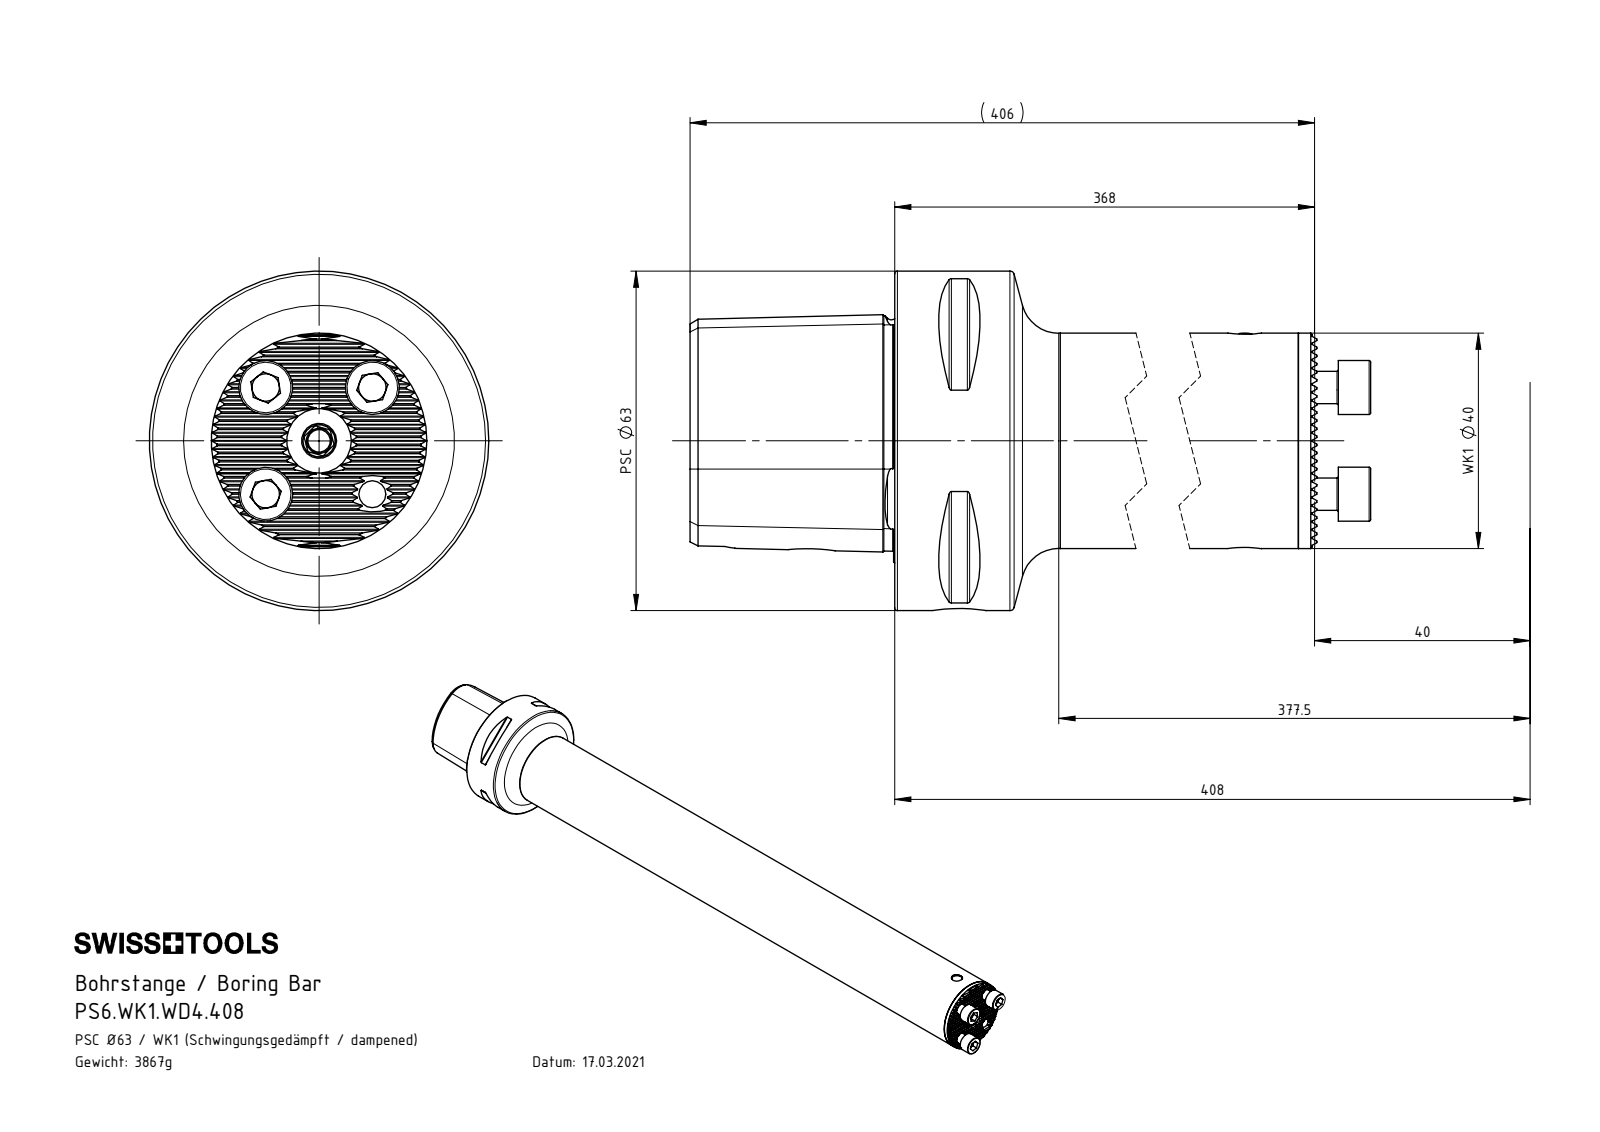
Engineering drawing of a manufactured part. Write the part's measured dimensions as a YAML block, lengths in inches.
part_name: "WD4-WK1.040.003_A; WD4-ER1.011.107_A; DIN 3771 - 31x2; WD4-ER1.035.019_A (+8 more)"
step_written_by: "SolidWorks 2017 (AUTOMOTIVE_DESIGN)"
units: inches
bodies: {solids: 16, faces: 532, planar: 267, cylindrical: 120, other: 145}
overall_size: [16.394, 2.48, 2.48]
volume: 30.38
surface_area: 199.1
round_holes:
  - {diameter: 0.197, count: 4}
  - {diameter: 0.236, count: 2}
  - {diameter: 0.165, count: 1}
  - {diameter: 0.276, count: 1}
  - {diameter: 0.291, count: 1}
  - {diameter: 0.319, count: 1}
  - {diameter: 0.335, count: 1}
  - {diameter: 0.394, count: 1}
  - {diameter: 0.472, count: 1}
  - {diameter: 0.551, count: 1}
  - {diameter: 0.709, count: 1}
  - {diameter: 0.827, count: 1}
round_bosses_or_shafts:
  - {diameter: 0.394, count: 3}
  - {diameter: 0.236, count: 3}
  - {diameter: 2.48, count: 1}
  - {diameter: 1.575, count: 1}
  - {diameter: 1.378, count: 1}
  - {diameter: 1.366, count: 1}
  - {diameter: 1.339, count: 1}
  - {diameter: 1.252, count: 1}
partial_cylinders:
  - {radius: 0.005, count: 27}
  - {radius: 0.02, count: 8}
  - {radius: 0.236, count: 1}
face_to_face_distances: [0.236, 4.661, 0.244, 4.654, 4.417, 13.701, 9.006, 13.431, 4.425, 4.695]
hole_center_spacings: [0.551, 0.78, 1.102, 1.083, 13.504, 14.587]
